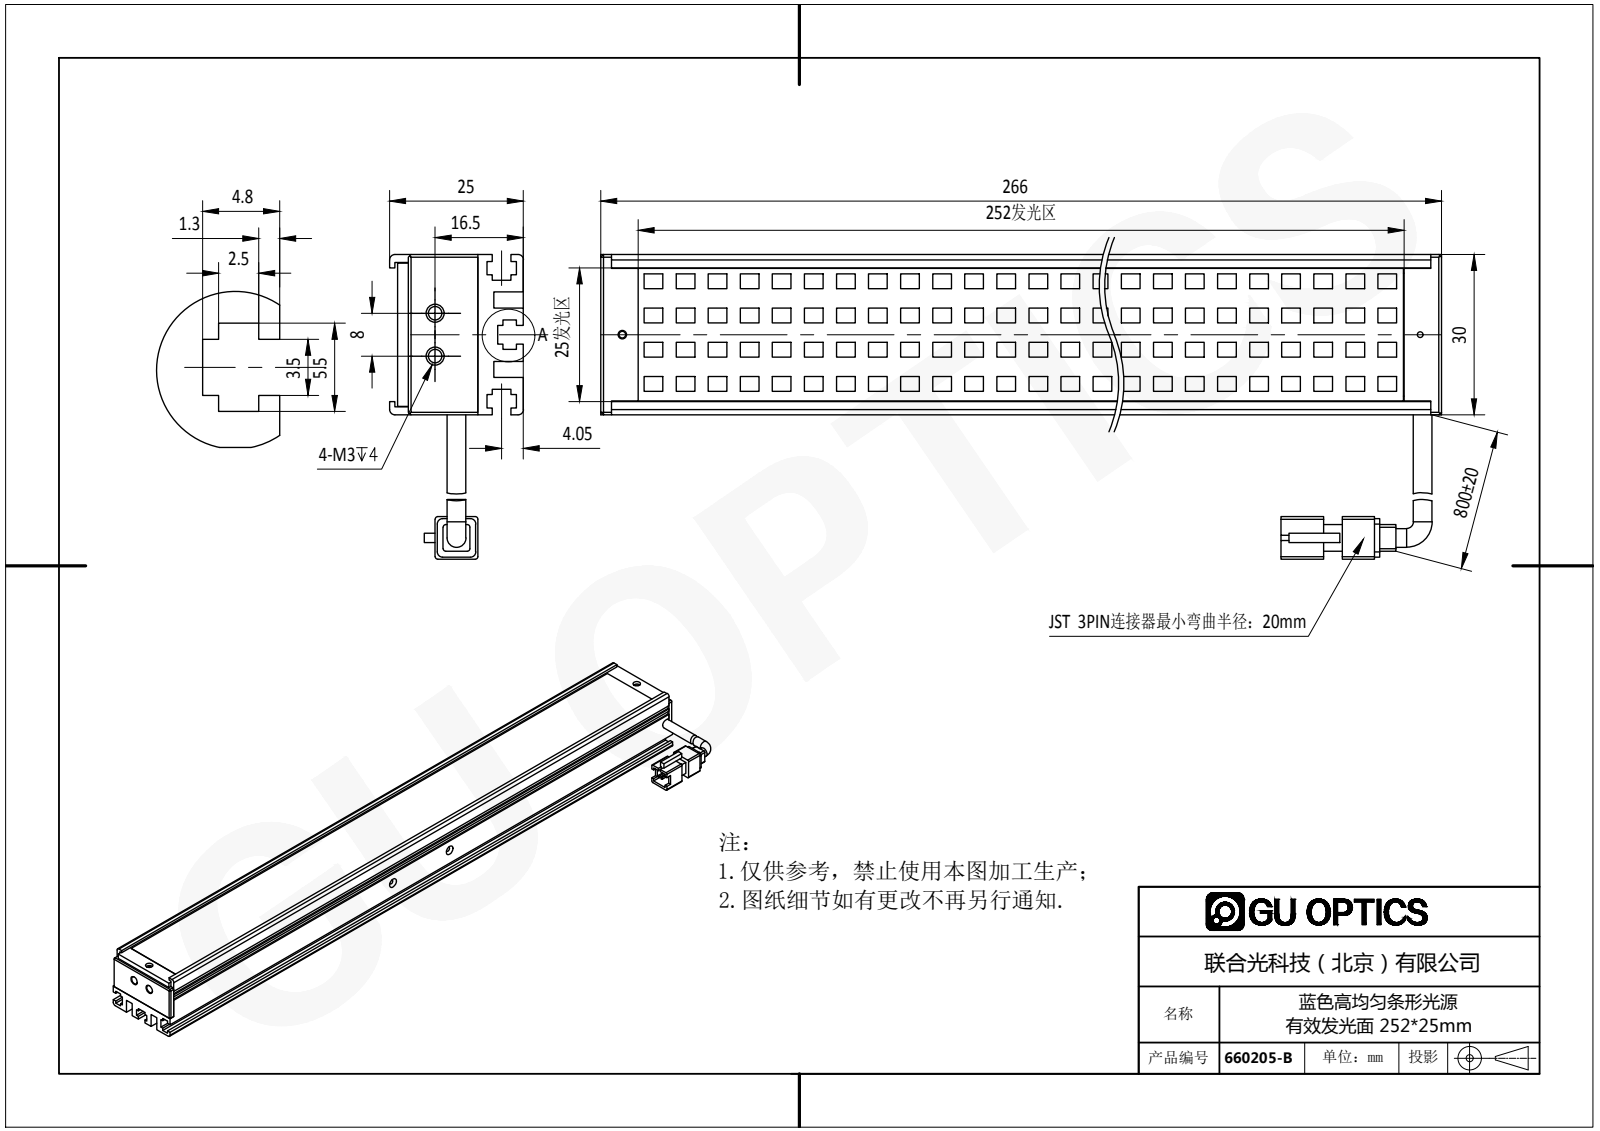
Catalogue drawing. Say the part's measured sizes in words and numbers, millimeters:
The part is named "660205-B". Its 3-D file was written by "SolidWorks 2016 (AUTOMOTIVE_DESIGN)". It is 6 solids with 1284 faces: 1098 planar, 83 cylindrical and 103 other. Overall it measures 266 by 57 by 25 millimeters. Its volume is 90 767 cubic millimeters and its surface area 92 489 square millimeters. Round holes: 5 of diameter 1.6, 2 of diameter 1.5, 2 of diameter 1.7, 2 of diameter 2.5, 2 of diameter 2.8, 2 of diameter 3, 1 of diameter 1.1, 1 of diameter 1.25, 1 of diameter 2. Round bosses or shafts: 2 of diameter 3.5. Partial cylindrical surfaces (rounded edges, fillets, slot ends): 12 of radius 1, 8 of radius 0.5, 1 of radius 1.65. The main face-to-face distances are 1, 13, 2, 2.5, 3, 27.5, 9.5, 4.5, 12, 15.1. The hole center spacings are 258, 7, 114, 114.19, 144, 144.15, 258.09, 8.
